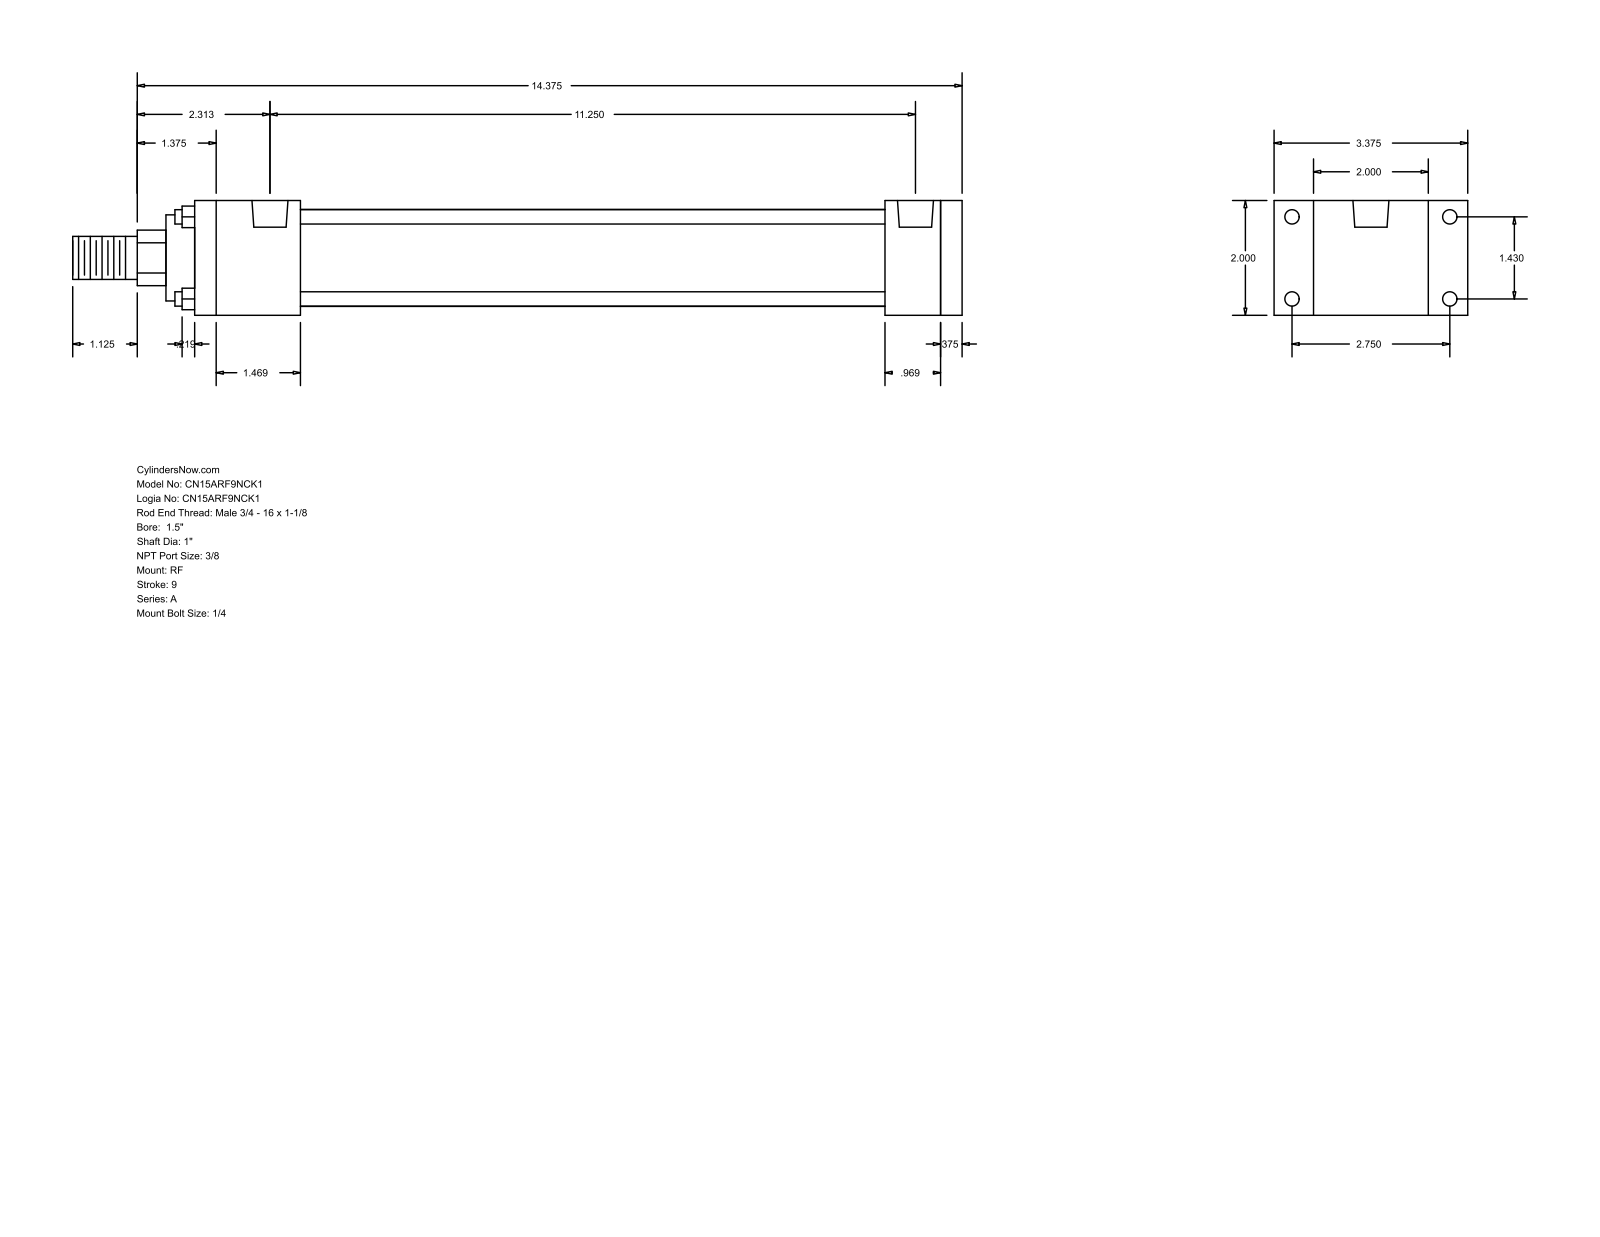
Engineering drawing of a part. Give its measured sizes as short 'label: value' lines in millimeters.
name: A_RF__0150_1
written by: GSSL Pune (CONFIG_CONTROL_DESIGN)
unit: mm
bodies: 0 solids, 92 faces (64 planar, 28 cylindrical, 0 other)
size: 393.7 × 85.72 × 50.8
holes: 4× ⌀5.56, 4× ⌀6.35, 2× ⌀15.93
bosses: 4× ⌀6.35, 1× ⌀42.93, 1× ⌀38.1, 1× ⌀25.4, 1× ⌀19.05
rounds: 1× R12.29
face distances: 50.8, 9.52, 330.2, 339.72, 305.59, 24.61, 34.13, 46.83, 258.76, 283.37
hole spacings: 3.97, 36.32, 69.84, 78.72, 277.81, 281.78, 285.75
